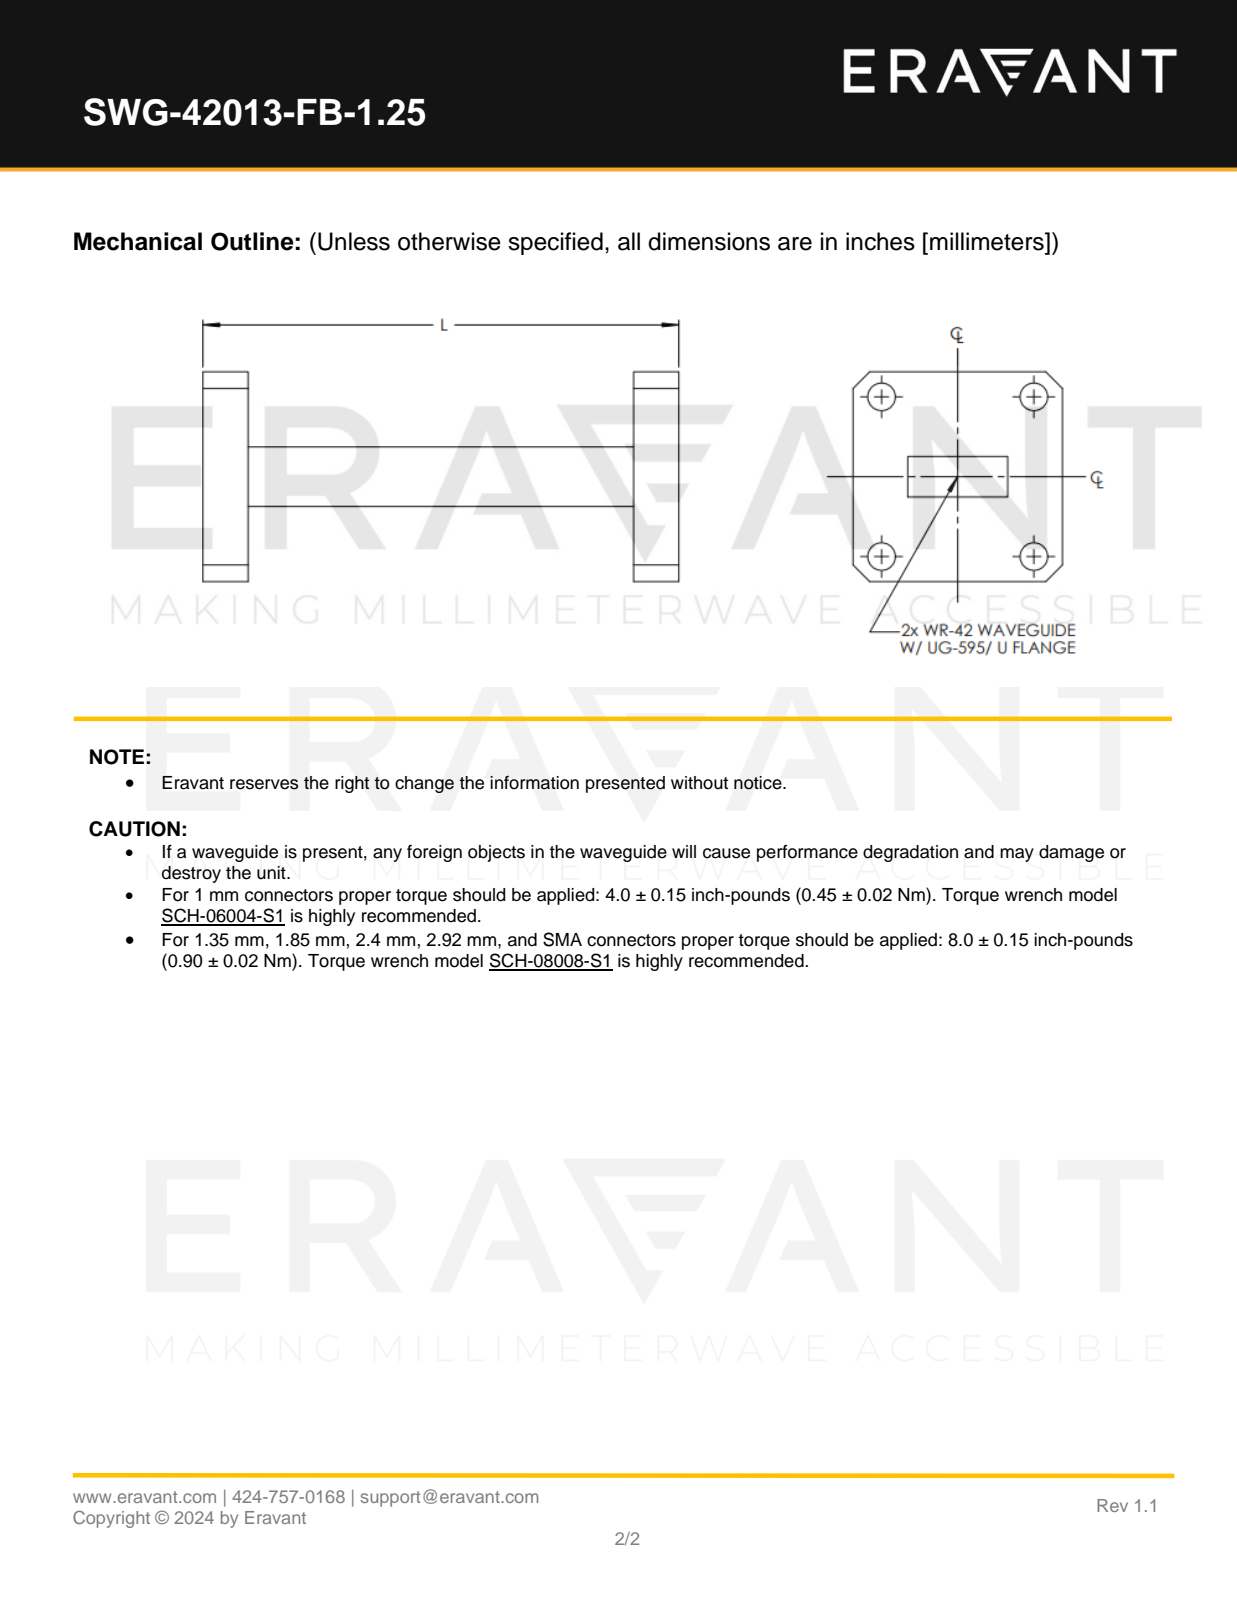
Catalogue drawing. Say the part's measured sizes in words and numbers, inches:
The part is named "SWG-42013-FB-1.25". Its 3-D file was written by "SolidWorks 2021 (CONFIG_CONTROL_DESIGN)". It is 1 solid with 50 faces: 34 planar, 16 cylindrical and 0 other. Overall it measures 1.25 by 0.88 by 0.88 inches. Its volume is 0.382 cubic inches and its surface area 5.797 square inches. Round holes: 4 of diameter 0.116. The main face-to-face distances are 0.19, 1.06, 1.25, 0.87, 0.88, 0.315, 0.565, 0.69, 0.25, 0.5. The hole center spacings are 0.64, 0.67, 0.927.
